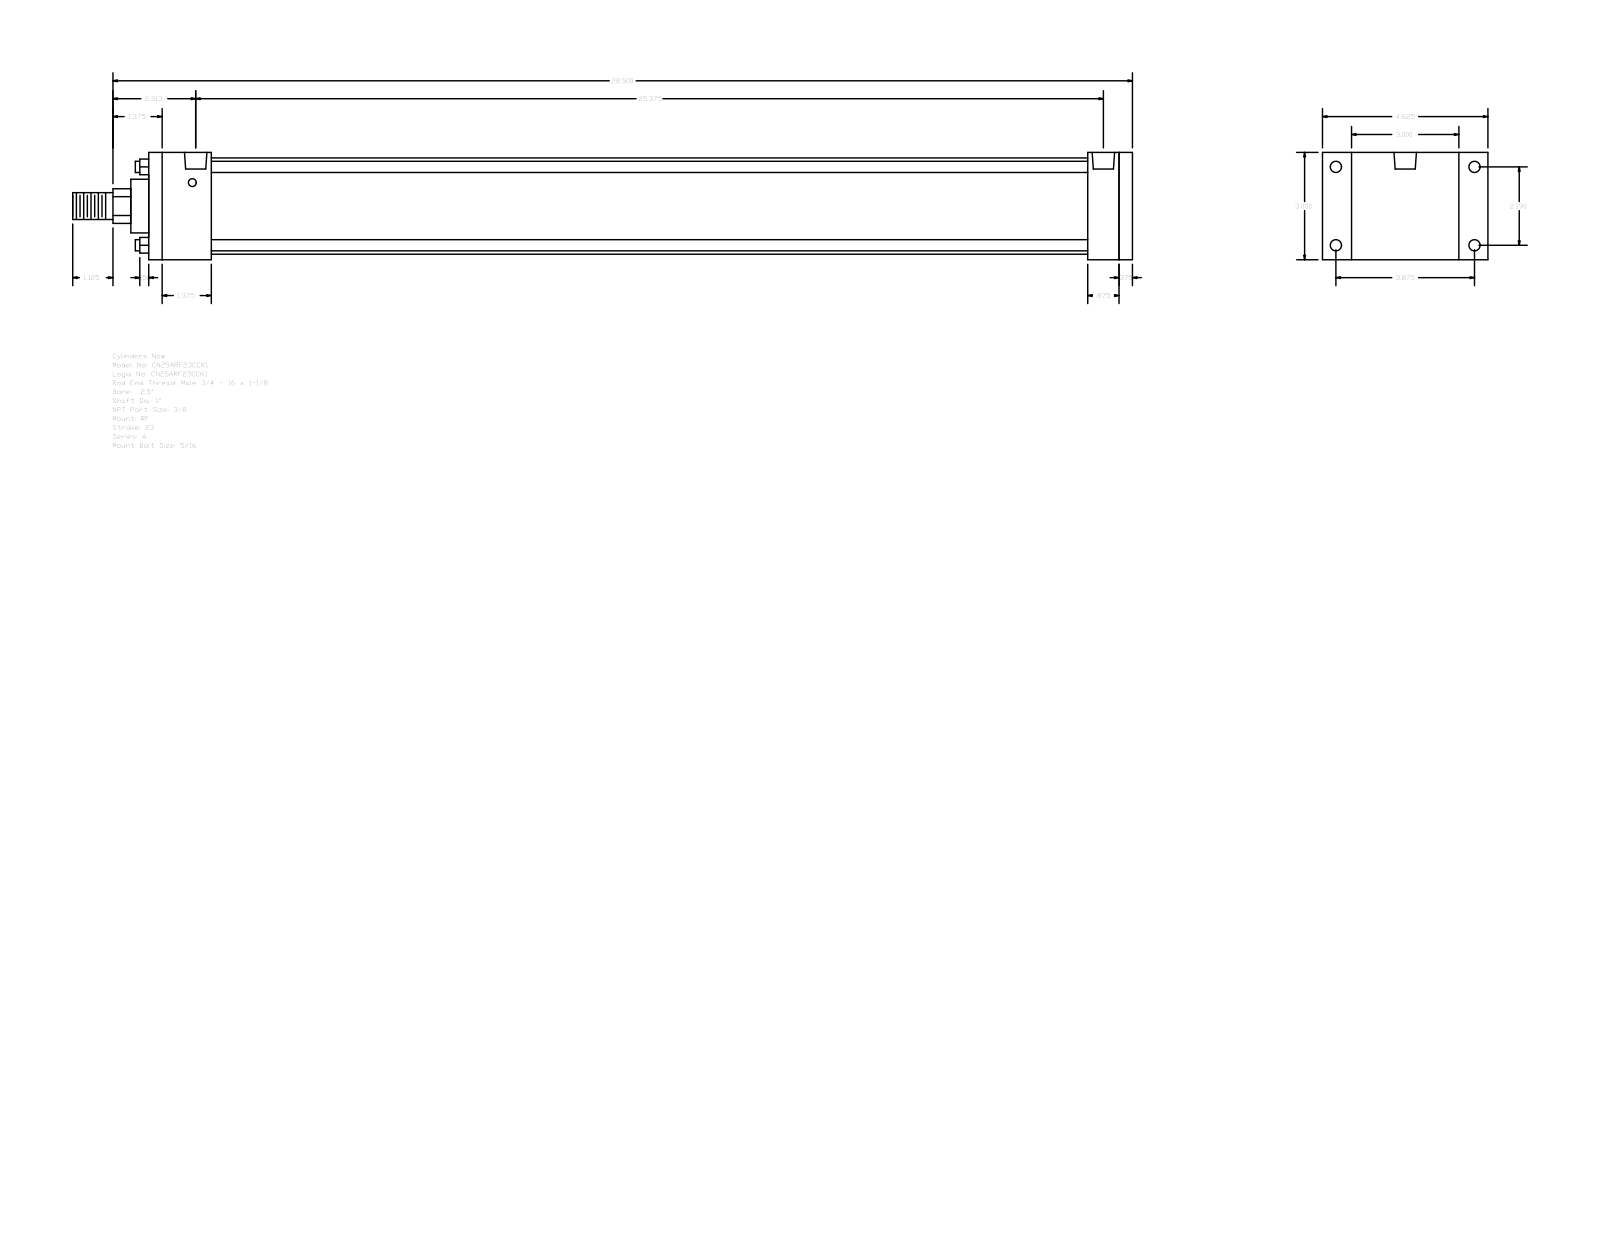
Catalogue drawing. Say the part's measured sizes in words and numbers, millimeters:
The part is named "A_RF__0250_1". Its 3-D file was written by "GSSL Pune (CONFIG_CONTROL_DESIGN)". It is 0 solids with 92 faces: 64 planar, 28 cylindrical and 0 other. Overall it measures 752.48 by 117.47 by 76.2 millimeters. Round holes: 4 of diameter 5.56, 4 of diameter 7.94, 2 of diameter 15.93. Round bosses or shafts: 4 of diameter 7.94, 1 of diameter 68.33, 1 of diameter 38.1, 1 of diameter 25.4, 1 of diameter 19.05. Partial cylindrical surfaces (rounded edges, fillets, slot ends): 1 of radius 12.29. The main face-to-face distances are 76.2, 698.5, 9.52, 688.98, 44.45, 666.75, 622.3, 644.53, 654.05, 22.23. The hole center spacings are 2.38, 55.62, 98.42, 113.05, 646.9, 649.28, 644.52.
